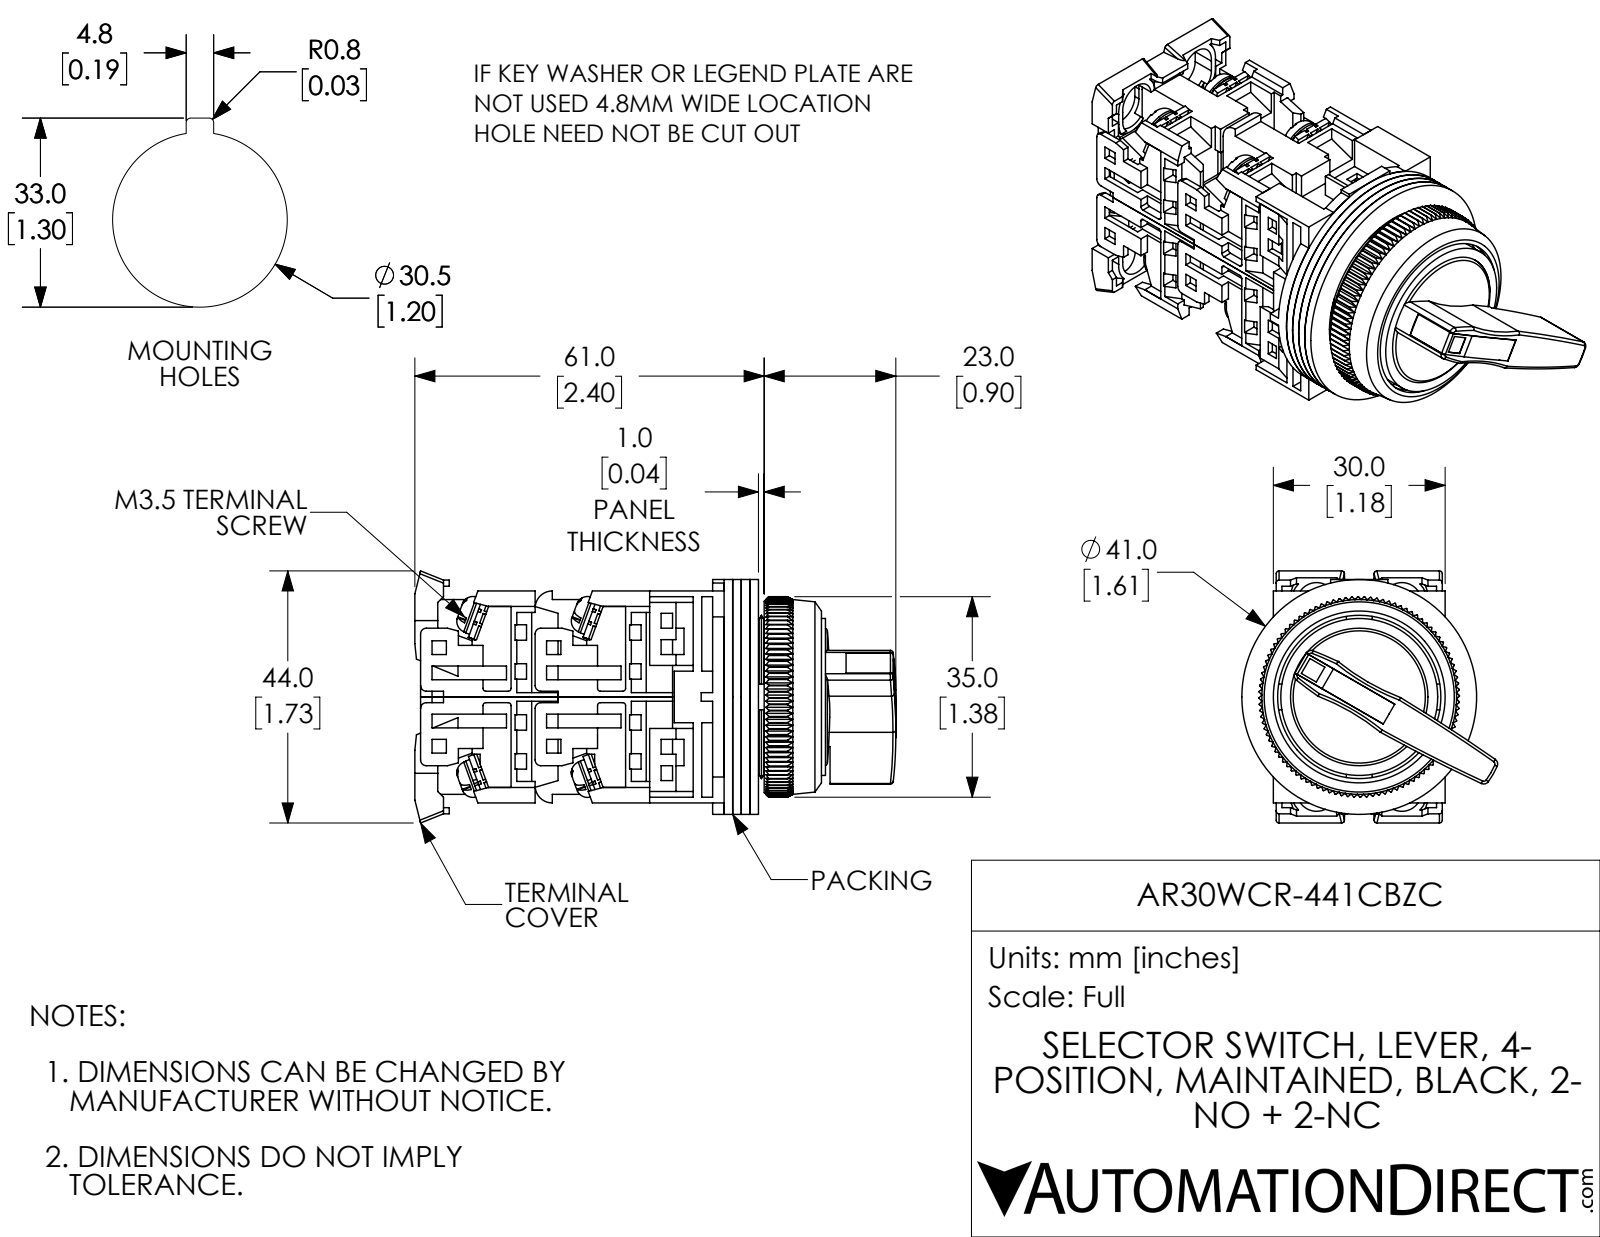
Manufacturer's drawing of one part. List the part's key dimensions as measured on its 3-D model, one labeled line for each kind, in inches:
Part name (STEP PRODUCT): AR30WCR-441CBZC
STEP written by: SolidWorks 2017 (AUTOMOTIVE_DESIGN)
Units: inches
Bodies: 40 solids, 2519 faces (1908 planar, 353 cylindrical, 258 other)
Overall size (bounding box): 3.307 × 1.759 × 1.732
Volume: 3.212 in³ · Surface area: 77.35 in²
Round holes (diameter × count): ⌀0.138 ×14, ⌀0.142 ×8, ⌀0.118 ×1, ⌀0.315 ×1, ⌀0.472 ×1, ⌀0.48 ×1, ⌀0.512 ×1, ⌀0.819 ×1, ⌀0.945 ×1, ⌀1.122 ×1, ⌀1.181 ×1, ⌀1.252 ×1
Round bosses / shafts (diameter × count): ⌀0.26 ×8, ⌀0.138 ×8, ⌀1.614 ×1, ⌀1.15 ×1, ⌀1.079 ×1, ⌀0.787 ×1, ⌀0.709 ×1, ⌀0.669 ×1
Partial cylindrical surfaces — rounded edges, fillets, slot ends (radius × count): R0.059 ×32, R0.02 ×17, R0.039 ×12, R0.118 ×4, R0.138 ×4, R0.177 ×4, R1.575 ×2, R1.638 ×2
Main face-to-face distances: 0.059, 0.118, 0.039, 0.787, 0.063, 0.177, 0.079, 0.02, 0.689, 0.028
Hole centre spacings: 0.579, 0.269, 0.638, 0.61
